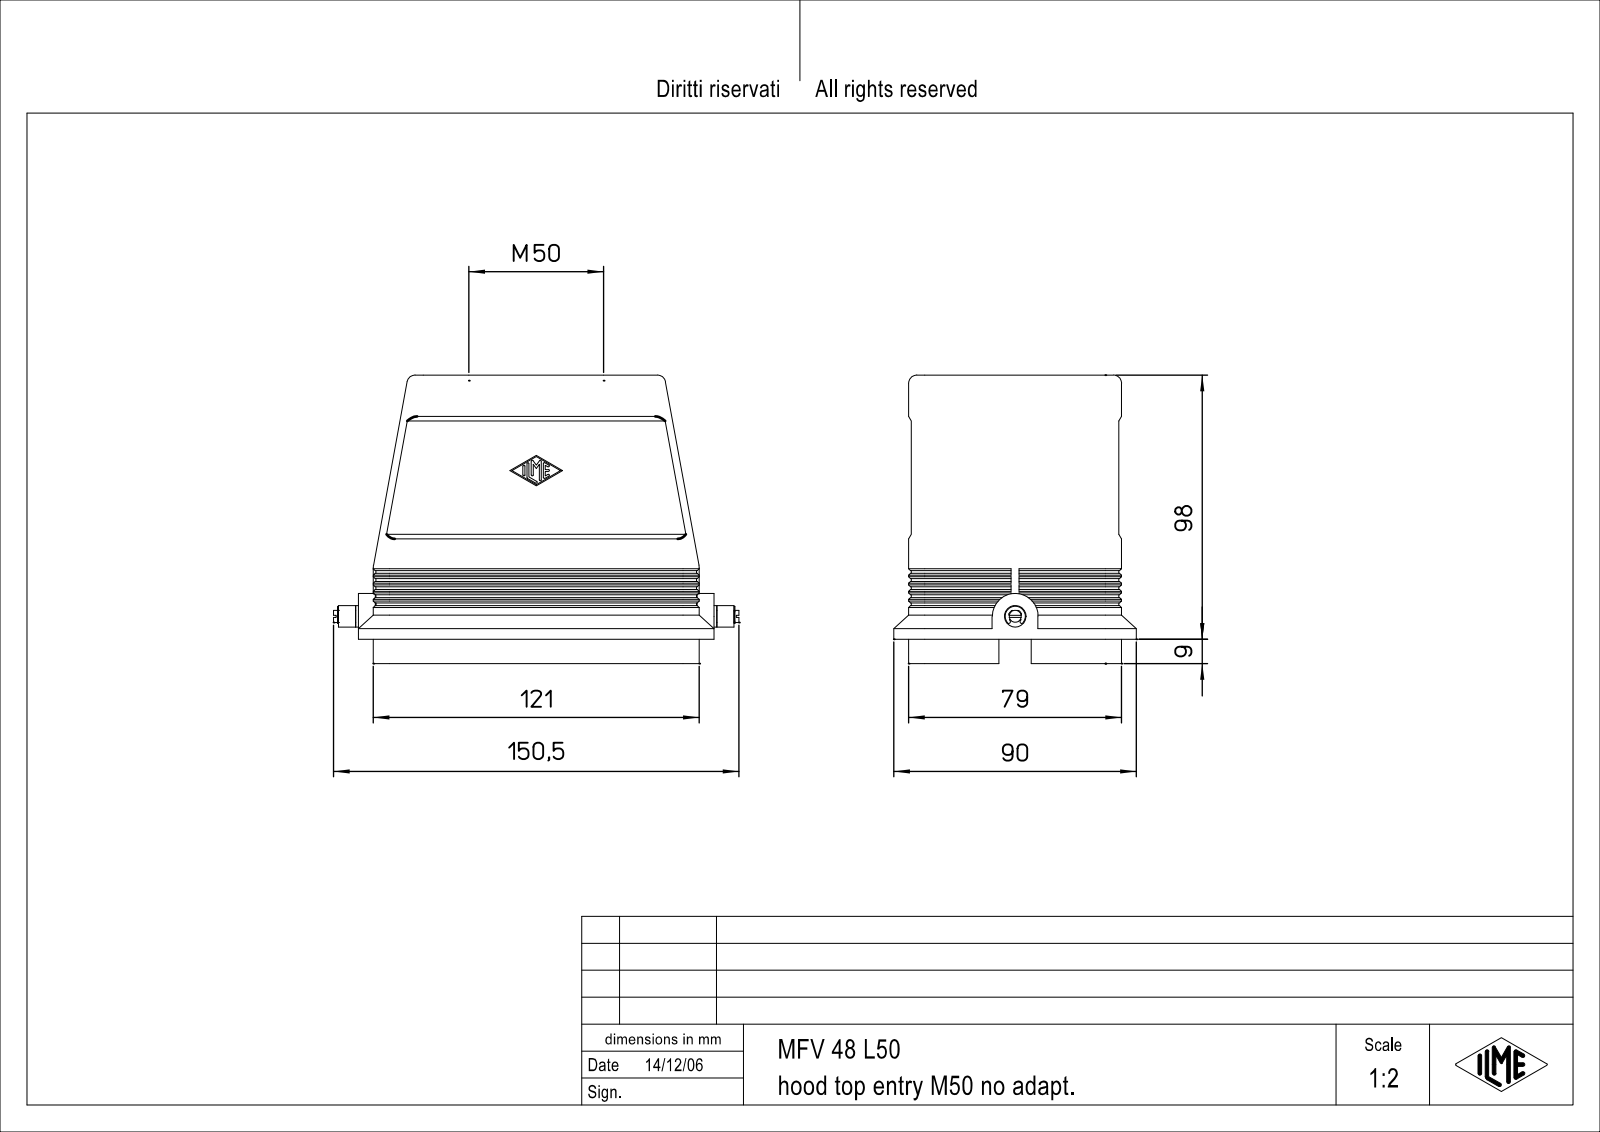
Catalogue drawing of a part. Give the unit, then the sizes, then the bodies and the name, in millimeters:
Units: millimetres
Overall size (bounding box): 150.5 × 118 × 90
Round holes (diameter × count): ⌀2.46 ×4, ⌀3.5 ×4, ⌀50 ×1, ⌀62 ×1
Round bosses / shafts (diameter × count): ⌀8 ×1, ⌀6 ×1, ⌀4.5 ×1, ⌀3.5 ×1
Partial cylindrical surfaces — rounded edges, fillets, slot ends (radius × count): R0.38 ×14, R2 ×12, R6 ×10, R0.5 ×4, R3 ×4, R11.5 ×4, R0.95 ×3, R0.62 ×2
Main face-to-face distances: 3.5, 72, 75.5, 1, 109, 2.5, 79, 74.5, 78, 9
Hole centre spacings: 27, 52.15, 60.54, 104, 107.45
Volume: 222 145 mm³ · Surface area: 105 627 mm²
Bodies: 1 solid, 672 faces (246 planar, 177 cylindrical, 249 other)
Part name (STEP PRODUCT): CH_MH Tüllengehäuse Verschluss für 1 Bügel 104_62 Teil 2
STEP written by: Autodesk Inventor 7 (AUTOMOTIVE_DESIGN)
